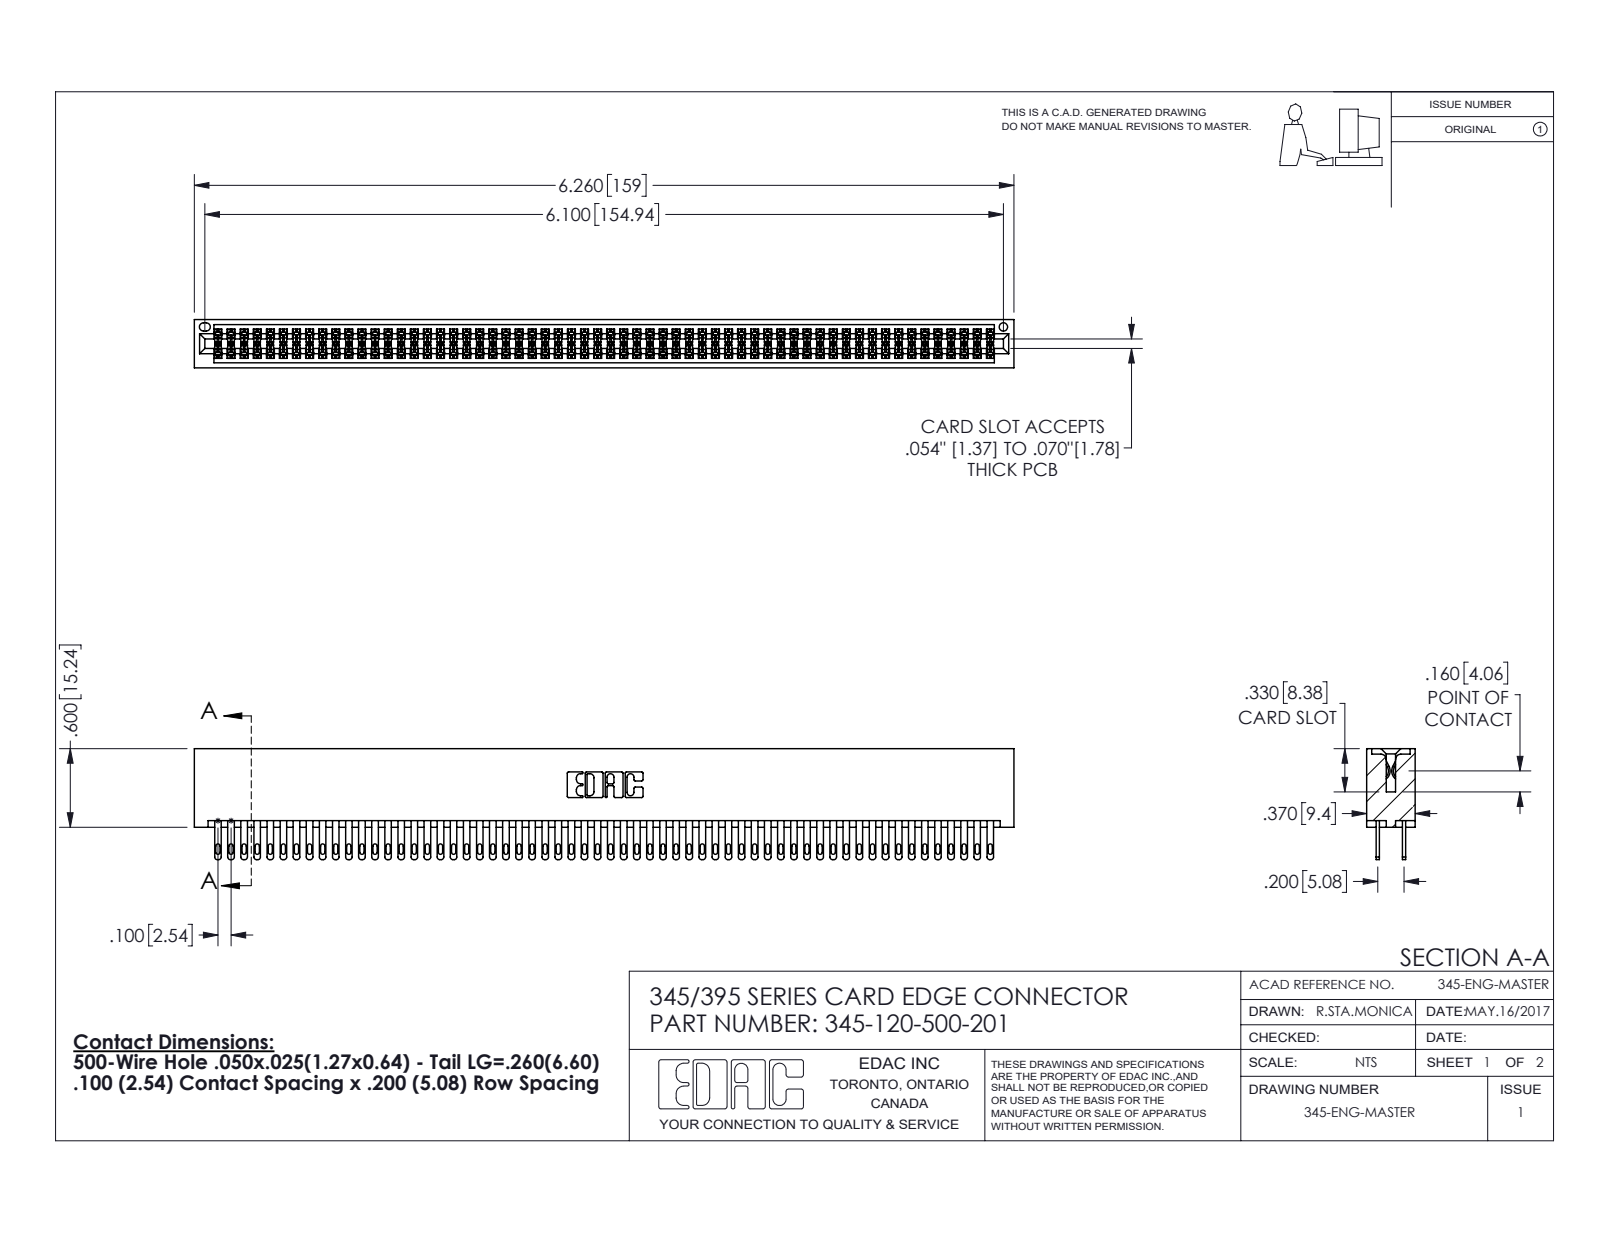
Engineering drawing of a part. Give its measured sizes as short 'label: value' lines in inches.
name: 345 Part_No Mounting Lugs; 345-292-001_345-293-100; 345-120-500-201
written by: SolidWorks 2016 (CONFIG_CONTROL_DESIGN)
unit: in
bodies: 121 solids, 5638 faces (3316 planar, 2322 cylindrical, 0 other)
size: 6.26 × 0.847 × 0.37
volume: 1.013 in³; area: 40.93 in²
holes: 1× ⌀0.064
rounds: 180× R0.006, 120× R0.016, 120× R0.02, 22× R0.01, 6× R0.007, 6× R0.031, 3× R0.026, 2× R0.014
face distances: 0.298, 0.072, 0.2, 0.098, 0.272, 0.025, 0.225, 0.37, 0.175, 0.149
